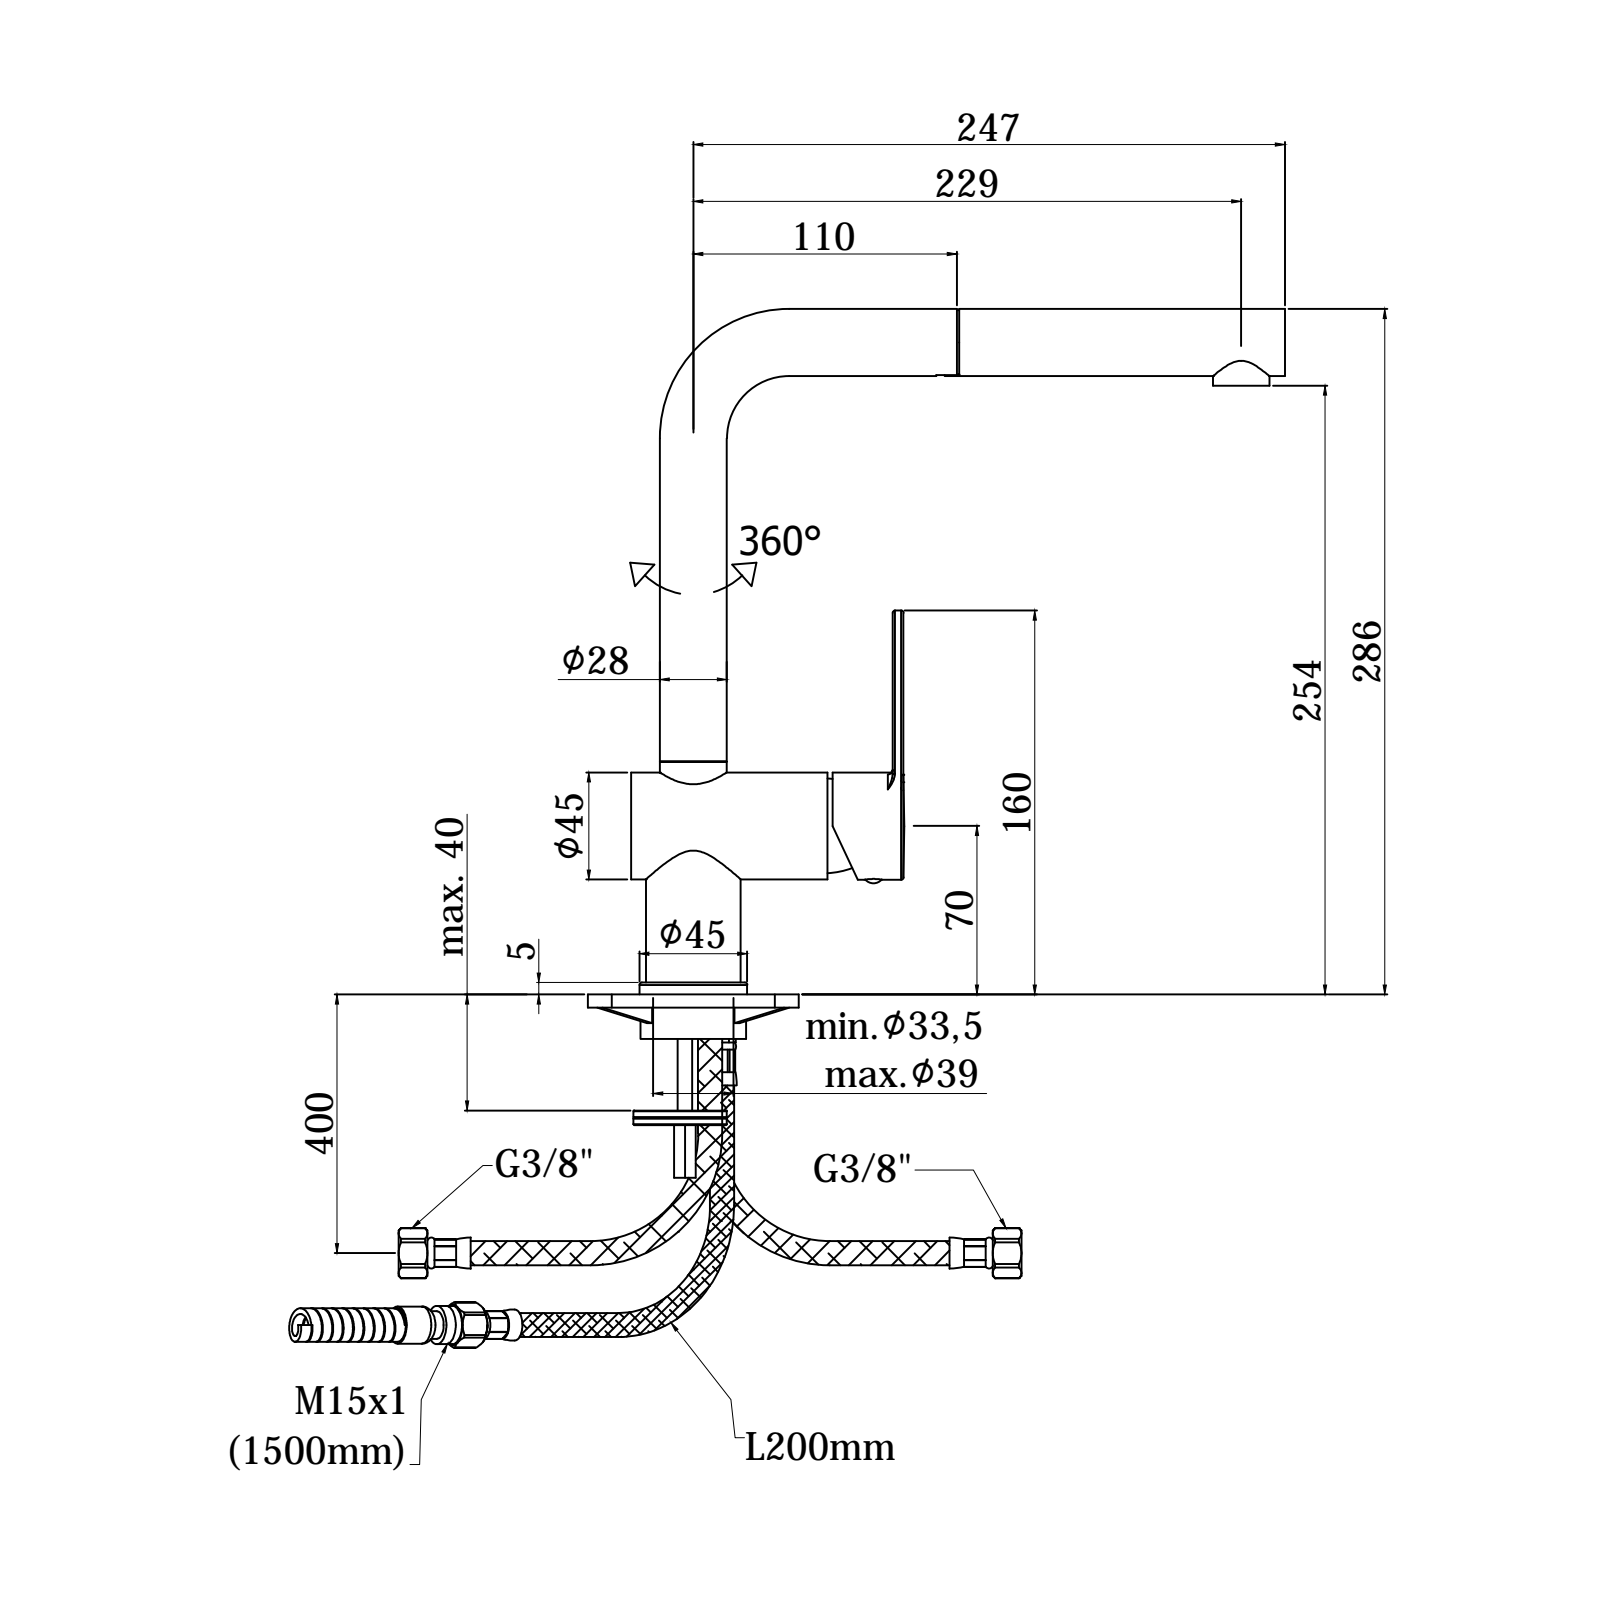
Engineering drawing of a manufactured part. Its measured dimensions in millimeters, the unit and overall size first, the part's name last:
Units: millimetres
Overall size (bounding box): 287 × 268.7 × 113.63
Round holes (diameter × count): ⌀0.4 ×480, ⌀6.5 ×3, ⌀7 ×3, ⌀8.6 ×3, ⌀9.4 ×3, ⌀5.5 ×2, ⌀25 ×2, ⌀25.7 ×2, ⌀36 ×2, ⌀3 ×1, ⌀3.4 ×1, ⌀3.5 ×1
Round bosses / shafts (diameter × count): ⌀28 ×2, ⌀23.5 ×2, ⌀20 ×2, ⌀18 ×2, ⌀45 ×1, ⌀44.8 ×1, ⌀44.7 ×1, ⌀39.6 ×1
Partial cylindrical surfaces — rounded edges, fillets, slot ends (radius × count): R0.2 ×72, R0.5 ×64, R0.3 ×27, R1 ×19, R24.3 ×12, R1.7 ×6, R2 ×6, R3 ×6
Main face-to-face distances: 3.5, 1.5, 70.8, 5, 5.95, 6.45, 11.2, 76.75, 15, 6.5
Hole centre spacings: 7.41, 10.48, 1.34, 4.69, 6.63, 9.49, 11.38, 13.25
Volume: 212 174 mm³ · Surface area: 173 636 mm²
Bodies: 1 solid, 4658 faces (2173 planar, 1782 cylindrical, 703 other)
Part name (STEP PRODUCT): RIN185CR
STEP written by: CREO PARAMETRIC BY PTC INC, 2020044 (CONFIG_CONTROL_DESIGN)
